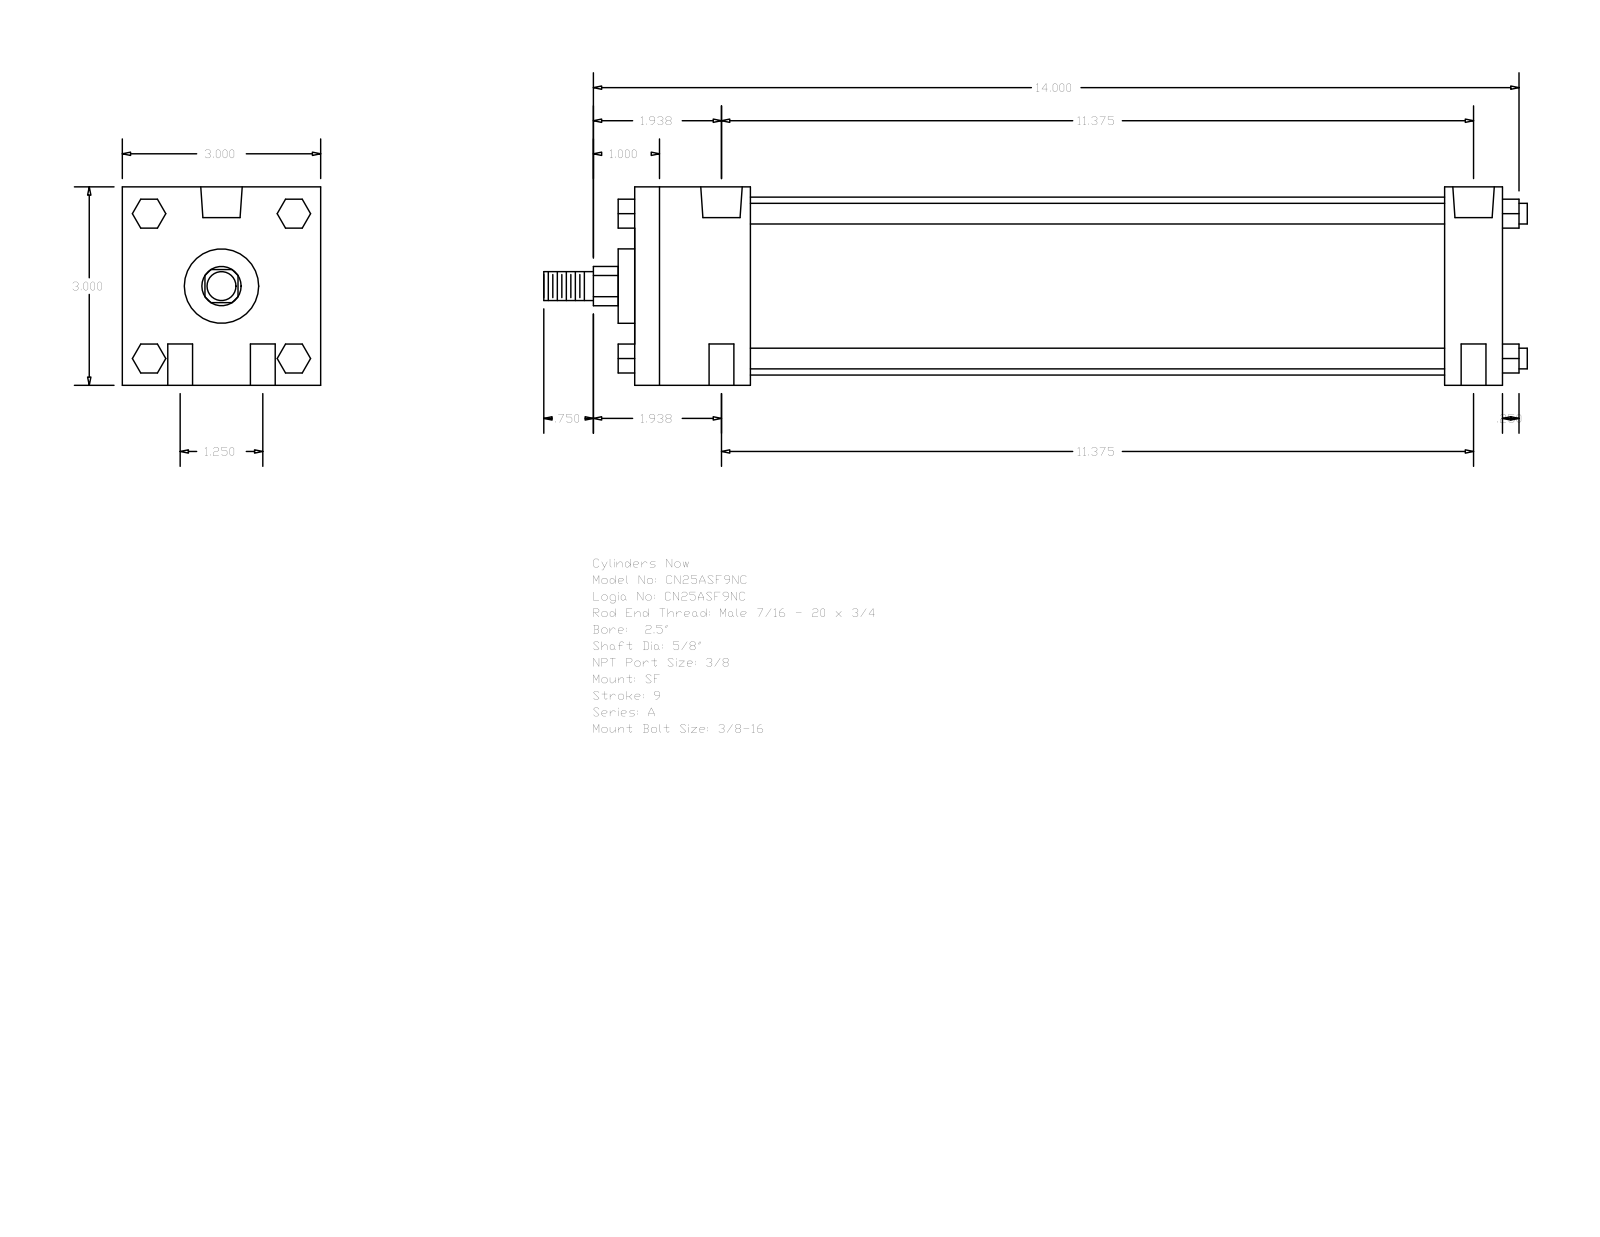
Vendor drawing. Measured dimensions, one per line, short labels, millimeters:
name: A_SF__0250_0.625
written by: GSSL Pune (CONFIG_CONTROL_DESIGN)
unit: mm
bodies: 0 solids, 124 faces (94 planar, 30 cylindrical, 0 other)
size: 377.82 × 76.2 × 76.2
holes: 4× ⌀9.53, 2× ⌀5.56, 2× ⌀15.93
bosses: 4× ⌀7.94, 1× ⌀68.33, 1× ⌀28.57, 1× ⌀15.88, 1× ⌀11.11
rounds: 1× R7.54
face distances: 76.2, 333.37, 44.45, 311.14, 22.23, 266.69, 288.92, 6.35, 339.72, 50.8
hole spacings: 15.88, 289.37, 288.93, 31.76, 290.67, 293.69
